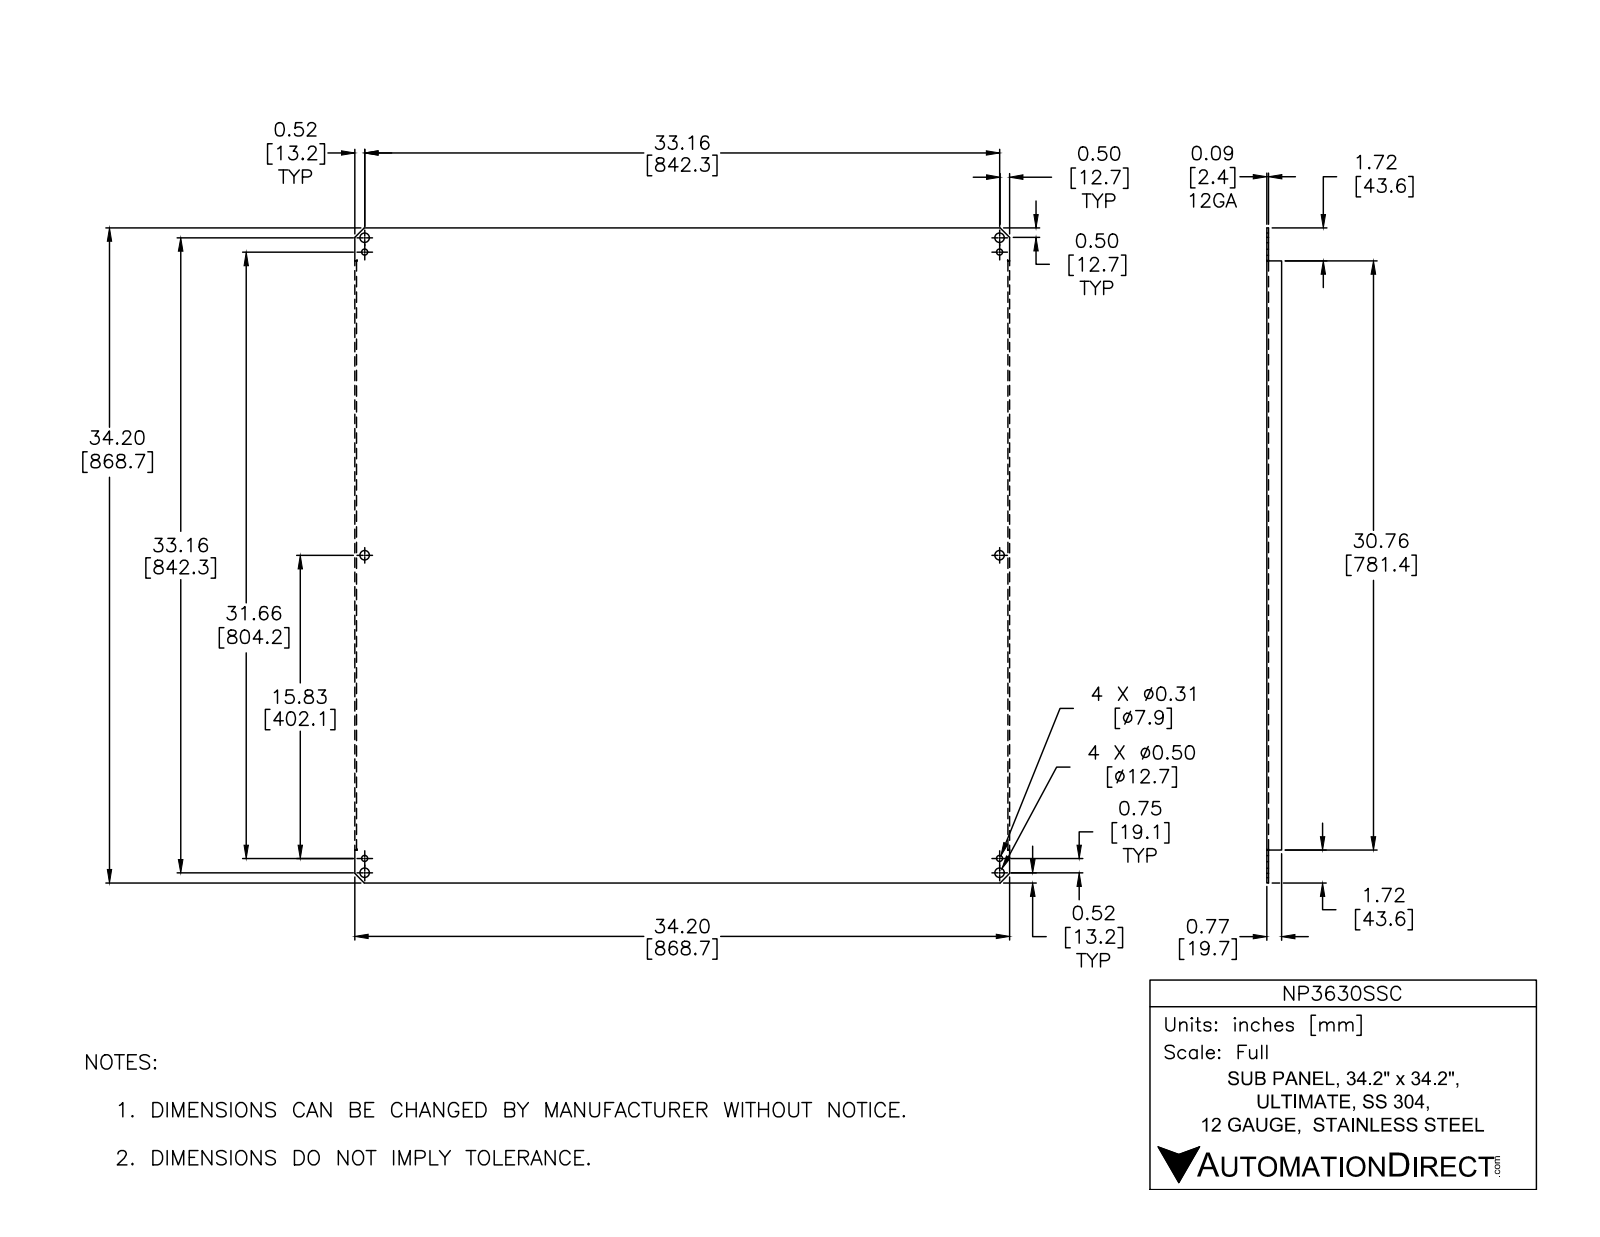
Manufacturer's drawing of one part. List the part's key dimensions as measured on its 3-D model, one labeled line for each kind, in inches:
Part name (STEP PRODUCT): NP3636SSC
STEP written by: Autodesk Inventor 2012 (AUTOMOTIVE_DESIGN)
Units: inches
Bodies: 1 solid, 70 faces (50 planar, 20 cylindrical, 0 other)
Overall size (bounding box): 34.2 × 34.2 × 0.774
Volume: 116.6 in³ · Surface area: 2 502 in²
Round holes (diameter × count): ⌀0.5 ×8, ⌀0.313 ×4
Partial cylindrical surfaces — rounded edges, fillets, slot ends (radius × count): R0.094 ×4, R0.188 ×4
Main face-to-face distances: 0.094, 34.106, 34.2, 34.013, 0.68, 0.774, 1.718, 32.482, 1.624, 32.388
Hole centre spacings: 16.58, 33.16, 37.074, 0.75, 15.83, 16.597, 23.448, 32.41
